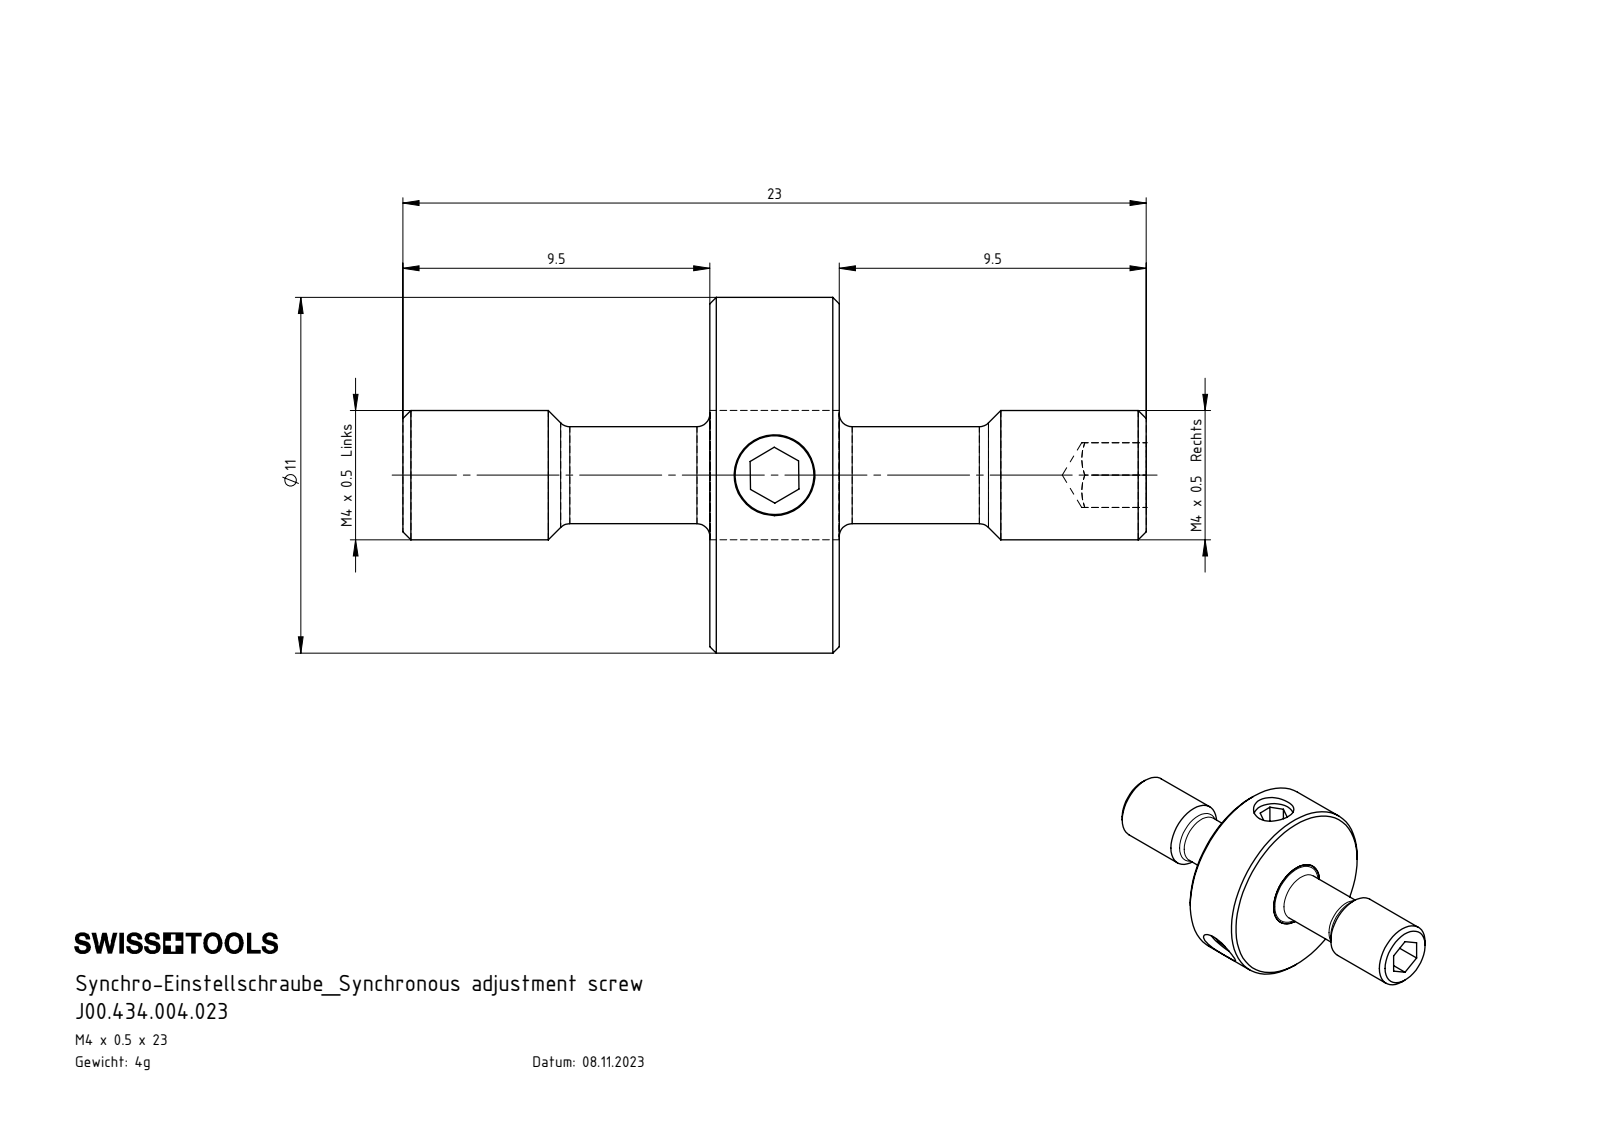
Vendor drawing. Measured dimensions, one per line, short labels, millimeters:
name: Z25-ER3.001.023_A; ISO 4026 - M3 x 3; Z25-ER3.002.004_A; J00.434.004.023
written by: SolidWorks 2022 (AUTOMOTIVE_DESIGN)
unit: mm
bodies: 5 solids, 99 faces (39 planar, 26 cylindrical, 34 other)
size: 23 × 11 × 11
volume: 553 mm³; area: 853 mm²
holes: 3× ⌀2.5
bosses: 4× ⌀3, 1× ⌀11, 1× ⌀4
face distances: 4, 9.5, 13.5, 1.5, 2, 3, 10.75, 12.25, 1.25, 2.75
